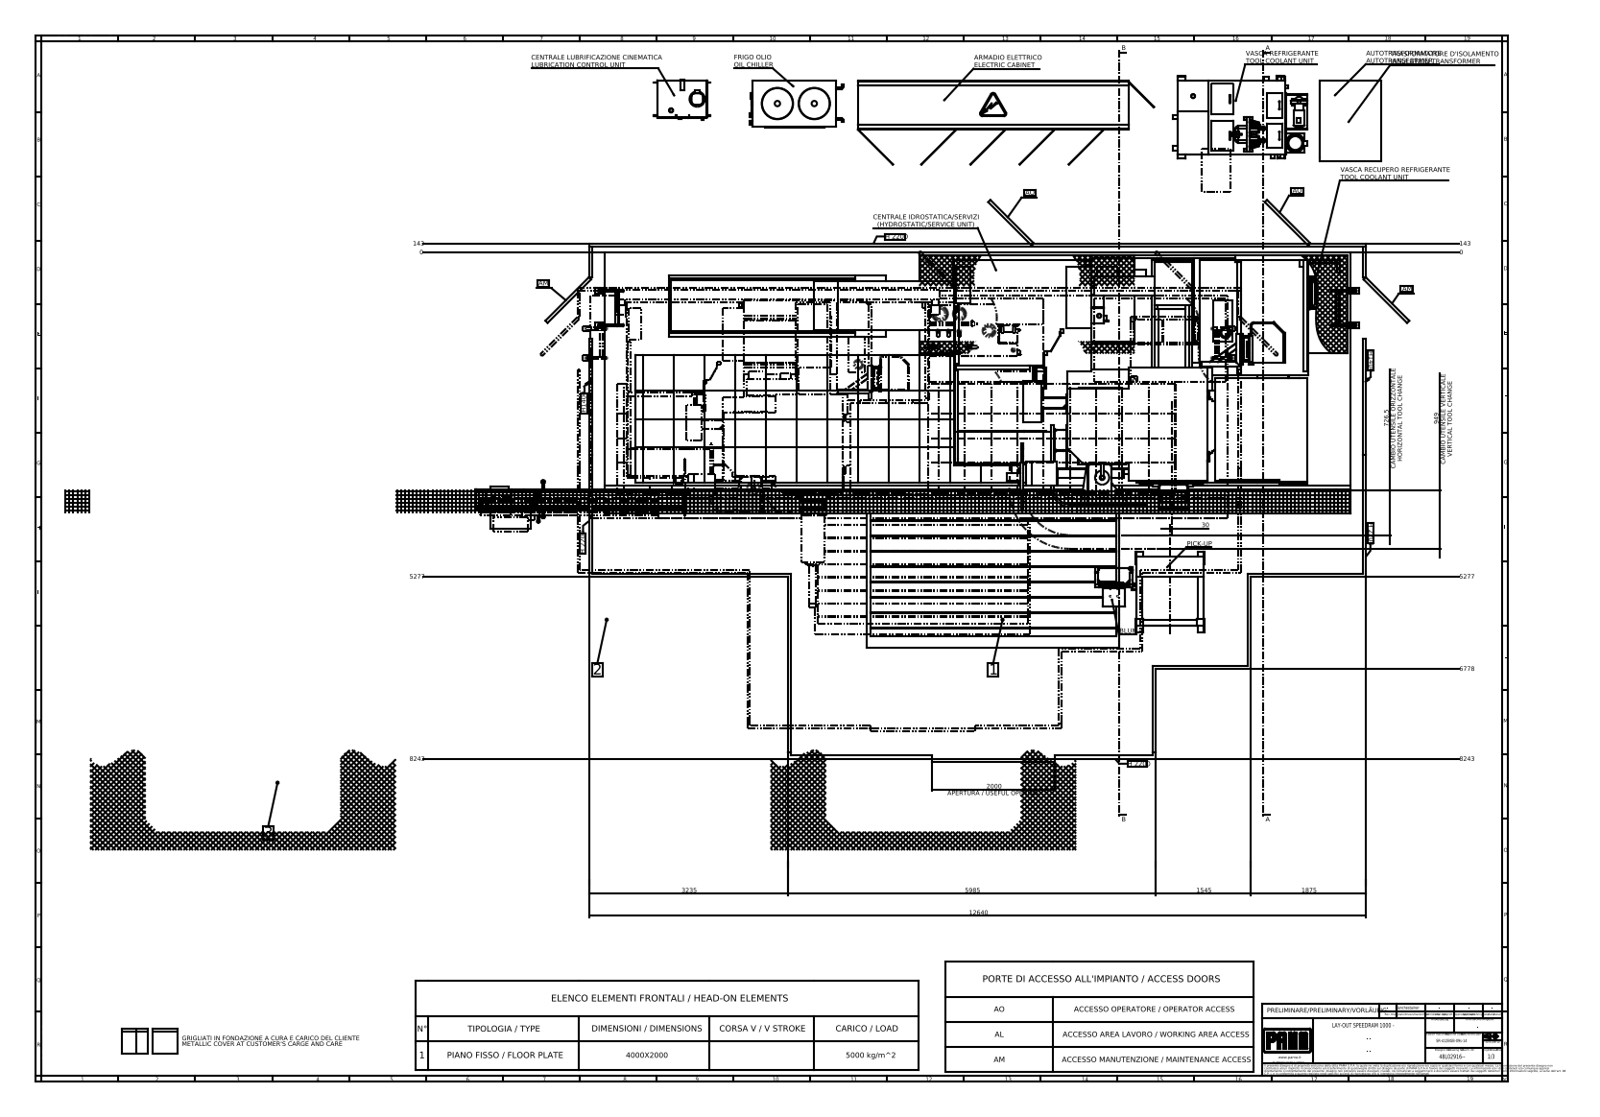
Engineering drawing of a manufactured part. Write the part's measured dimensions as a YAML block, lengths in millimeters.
part_name: "S002727_INTERASSE=1000; S002841; S003304; S001576_DEFAULT<A macchina> (+8 more)"
step_written_by: "SolidWorks 2023 (AUTOMOTIVE_DESIGN)"
units: millimeters
bodies: {solids: 401, faces: 6304, planar: 4429, cylindrical: 1421, other: 454}
overall_size: [16140, 14057.4, 7912.5]
volume: 412000000000
surface_area: 1601000000
round_holes:
  - {diameter: 35, count: 64}
  - {diameter: 69.6, count: 63}
  - {diameter: 37.2, count: 18}
  - {diameter: 30, count: 9}
  - {diameter: 13, count: 8}
  - {diameter: 14, count: 8}
  - {diameter: 8, count: 6}
  - {diameter: 12.5, count: 4}
  - {diameter: 56.66, count: 4}
  - {diameter: 60, count: 4}
  - {diameter: 25.6, count: 3}
  - {diameter: 50, count: 3}
round_bosses_or_shafts:
  - {diameter: 42.4, count: 18}
  - {diameter: 20, count: 14}
  - {diameter: 40, count: 11}
  - {diameter: 9, count: 10}
  - {diameter: 55, count: 8}
  - {diameter: 66.3, count: 7}
  - {diameter: 60, count: 6}
  - {diameter: 35, count: 6}
partial_cylinders:
  - {radius: 5, count: 128}
  - {radius: 15, count: 53}
  - {radius: 8, count: 52}
  - {radius: 35, count: 26}
  - {radius: 6, count: 25}
  - {radius: 3, count: 21}
  - {radius: 4, count: 21}
  - {radius: 10, count: 20}
face_to_face_distances: [2000, 50, 1247, 753, 5, 10, 13986, 16140, 2650, 2700]
hole_center_spacings: [273.13, 500, 1235.56, 758.02, 1423.59, 1000, 130, 260]
